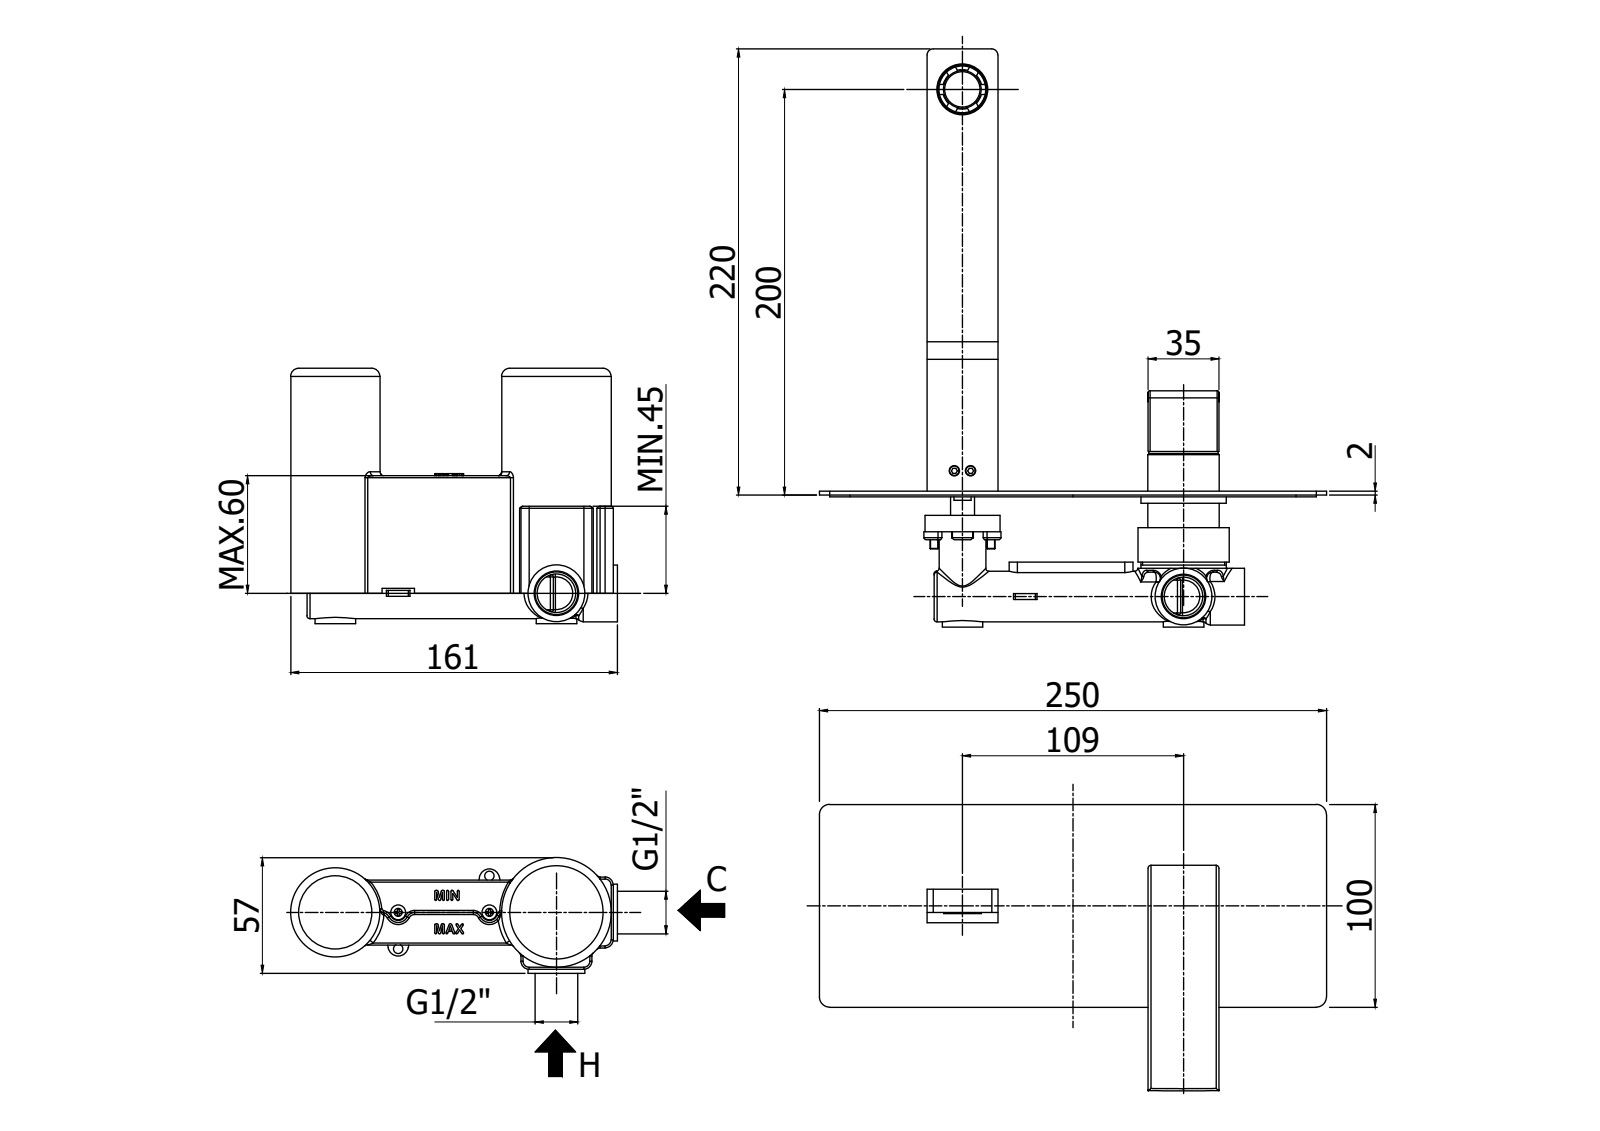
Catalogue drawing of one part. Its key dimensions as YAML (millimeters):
part_name: "EL105CR"
step_written_by: "CREO PARAMETRIC BY PTC INC, 2020044 (CONFIG_CONTROL_DESIGN)"
units: millimeters
bodies: {solids: 2, faces: 129, planar: 45, cylindrical: 52, other: 32}
overall_size: [250, 220, 141.72]
volume: 182585
surface_area: 92902
round_holes:
  - {diameter: 4.5, count: 1}
  - {diameter: 5.5, count: 1}
  - {diameter: 7.8, count: 1}
  - {diameter: 24.8, count: 1}
  - {diameter: 26.2, count: 1}
  - {diameter: 27, count: 1}
  - {diameter: 28, count: 1}
  - {diameter: 29, count: 1}
  - {diameter: 30.6, count: 1}
  - {diameter: 31.7, count: 1}
round_bosses_or_shafts:
  - {diameter: 35.2, count: 1}
  - {diameter: 18.5, count: 1}
partial_cylinders:
  - {radius: 1, count: 13}
  - {radius: 1.5, count: 8}
  - {radius: 5, count: 5}
  - {radius: 3, count: 2}
face_to_face_distances: [2, 11.5, 48.28, 46.28, 35, 44.28, 42.28, 4, 5, 16.5]
